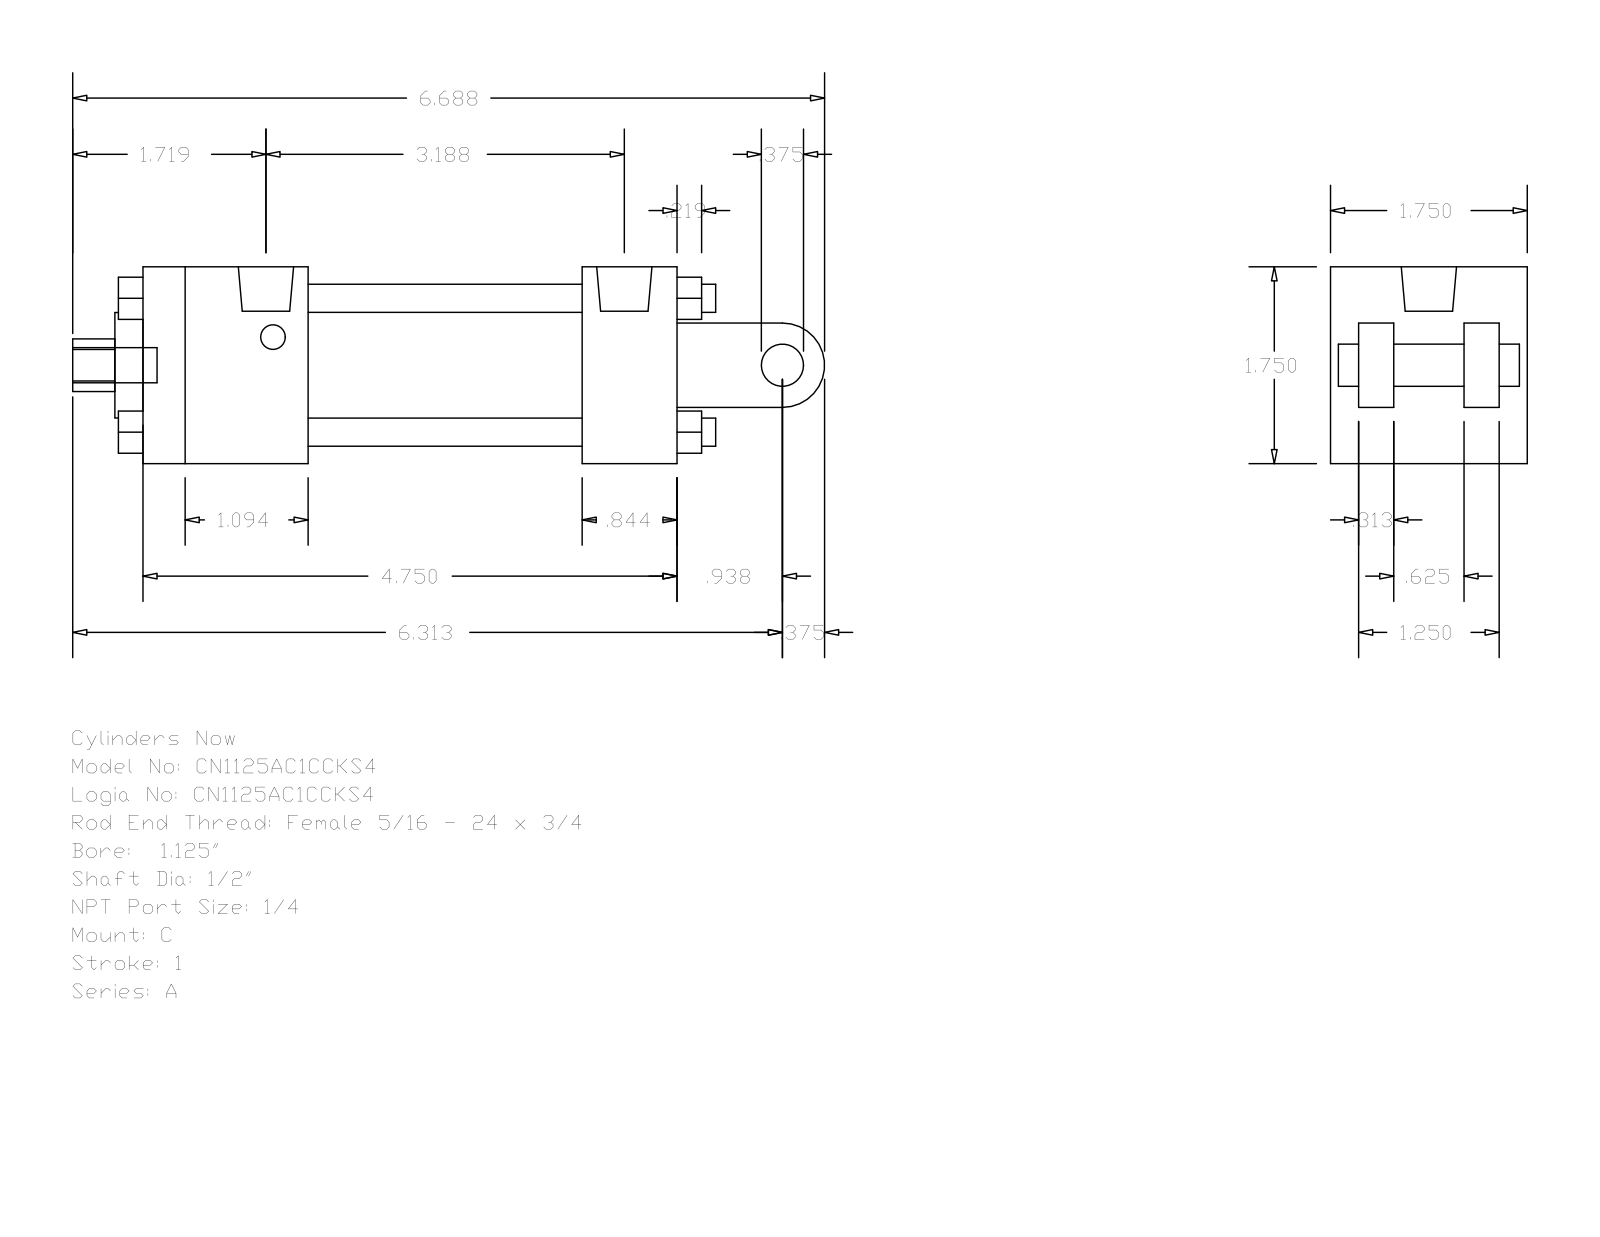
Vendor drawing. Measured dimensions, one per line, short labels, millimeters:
name: A_C__0112_0.5
written by: GSSL Pune (CONFIG_CONTROL_DESIGN)
unit: mm
bodies: 0 solids, 135 faces (102 planar, 33 cylindrical, 0 other)
size: 169.86 × 44.45 × 44.45
holes: 2× ⌀5.56, 1× ⌀12.49, 1× ⌀12.7, 1× ⌀23.81, 1× ⌀31.88
bosses: 4× ⌀6.35, 2× ⌀5.56, 1× ⌀12.49, 1× ⌀9.53, 1× ⌀7.94
rounds: 1× R5.94, 1× R9.53
face distances: 44.46, 6.35, 31.76, 14.29, 120.65, 30.17, 99.21, 21.44, 37.3, 61.91
hole spacings: 1.59
